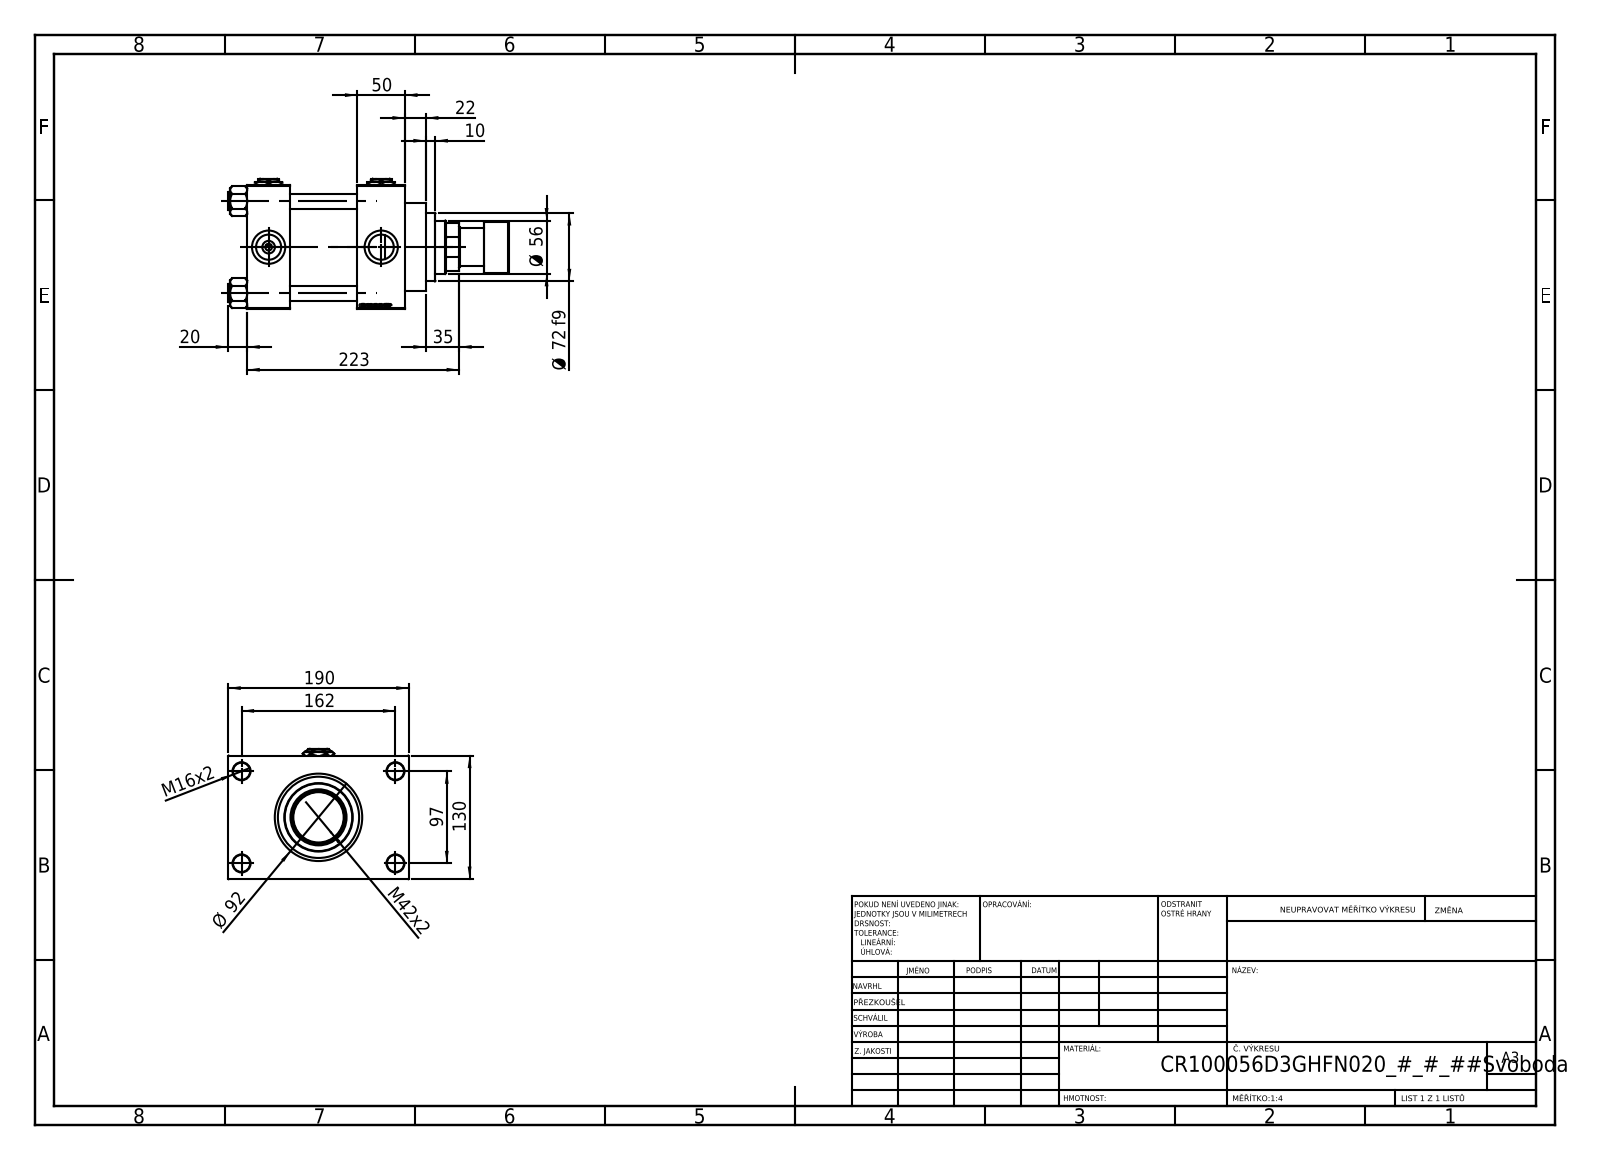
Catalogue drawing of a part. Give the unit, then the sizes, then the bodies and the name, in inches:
Units: inches
Overall size (bounding box): 11.614 × 7.48 × 5.394
Round holes (diameter × count): ⌀0.63 ×4, ⌀0.709 ×4, ⌀1.041 ×4, ⌀1.378 ×4, ⌀0.276 ×3, ⌀1.594 ×1, ⌀2.205 ×1, ⌀2.323 ×1, ⌀2.992 ×1, ⌀3.366 ×1, ⌀3.937 ×1
Round bosses / shafts (diameter × count): ⌀0.748 ×4, ⌀4.173 ×1, ⌀3.622 ×1, ⌀2.835 ×1, ⌀2.126 ×1, ⌀1.575 ×1
Main face-to-face distances: 5.118, 4.567, 1.969, 1.772, 2.795, 6.535, 4.764, 1.181, 6.299, 2.008
Hole centre spacings: 1.281, 2.698, 3.717, 3.815, 4.026, 5.096, 6.367, 3.819
Volume: 165.1 in³ · Surface area: 591.8 in²
Bodies: 14 solids, 1266 faces (597 planar, 103 cylindrical, 566 other)
Part name (STEP PRODUCT): Zatka_pro_OIL_PORT; V215CR_VCP_D; NUT_M5_D; V215CR_ROD_END_F (+3 more)
STEP written by: SolidWorks 2019 (CONFIG_CONTROL_DESIGN)
